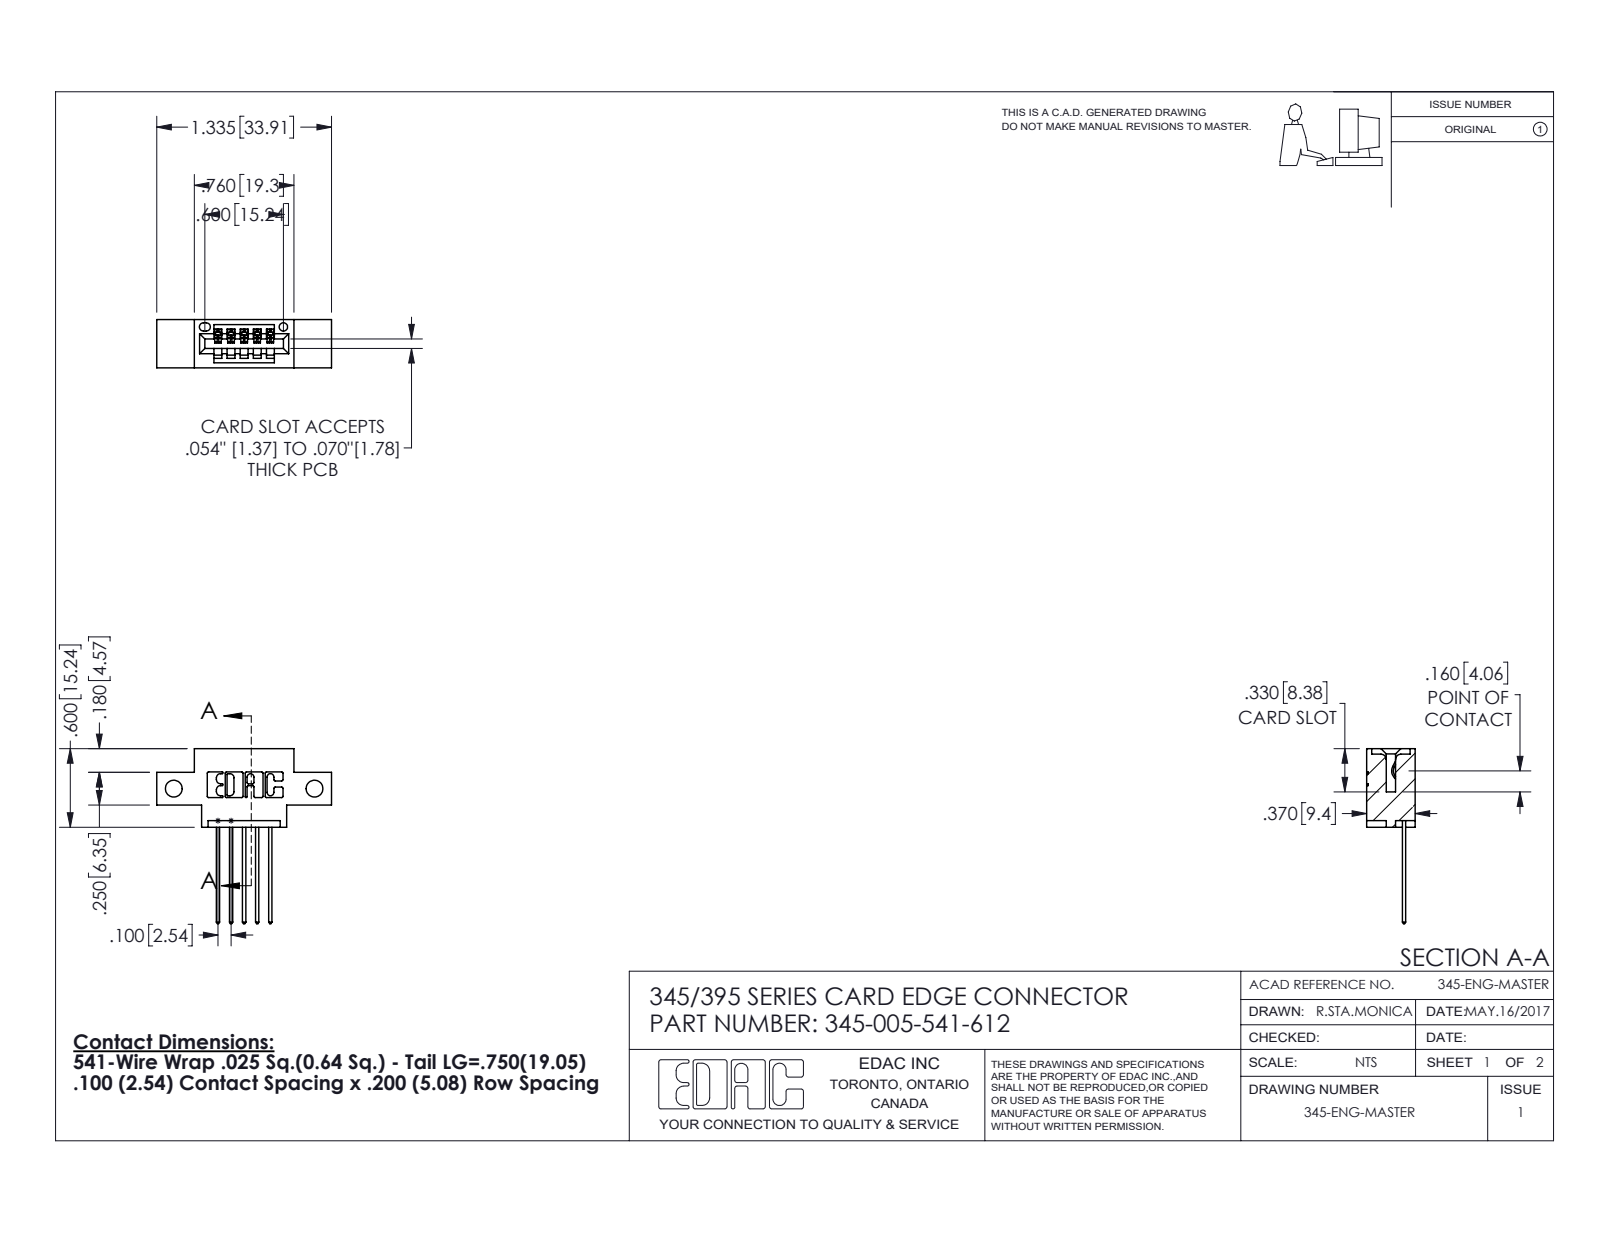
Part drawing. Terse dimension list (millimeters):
name: 345-292-001_345-293-141; 345 Part_0.170 Offset - Side Mount; 345-005-541-612
written by: SolidWorks 2016 (CONFIG_CONTROL_DESIGN)
unit: mm
bodies: 6 solids, 420 faces (284 planar, 136 cylindrical, 0 other)
size: 34 × 33.9 × 9.4
volume: 2 740 mm³; area: 3 211 mm²
holes: 2× ⌀3.3, 1× ⌀1.6
rounds: 22× R0.3, 10× R0.2, 10× R0.3, 6× R0.2, 6× R0.8, 3× R0.7, 2× R0.8, 2× R1
face distances: 9.4, 5.1, 7.6, 1.8, 2.5, 0.6, 2.5, 6.9, 6.4, 1.5
hole spacings: 27.3
